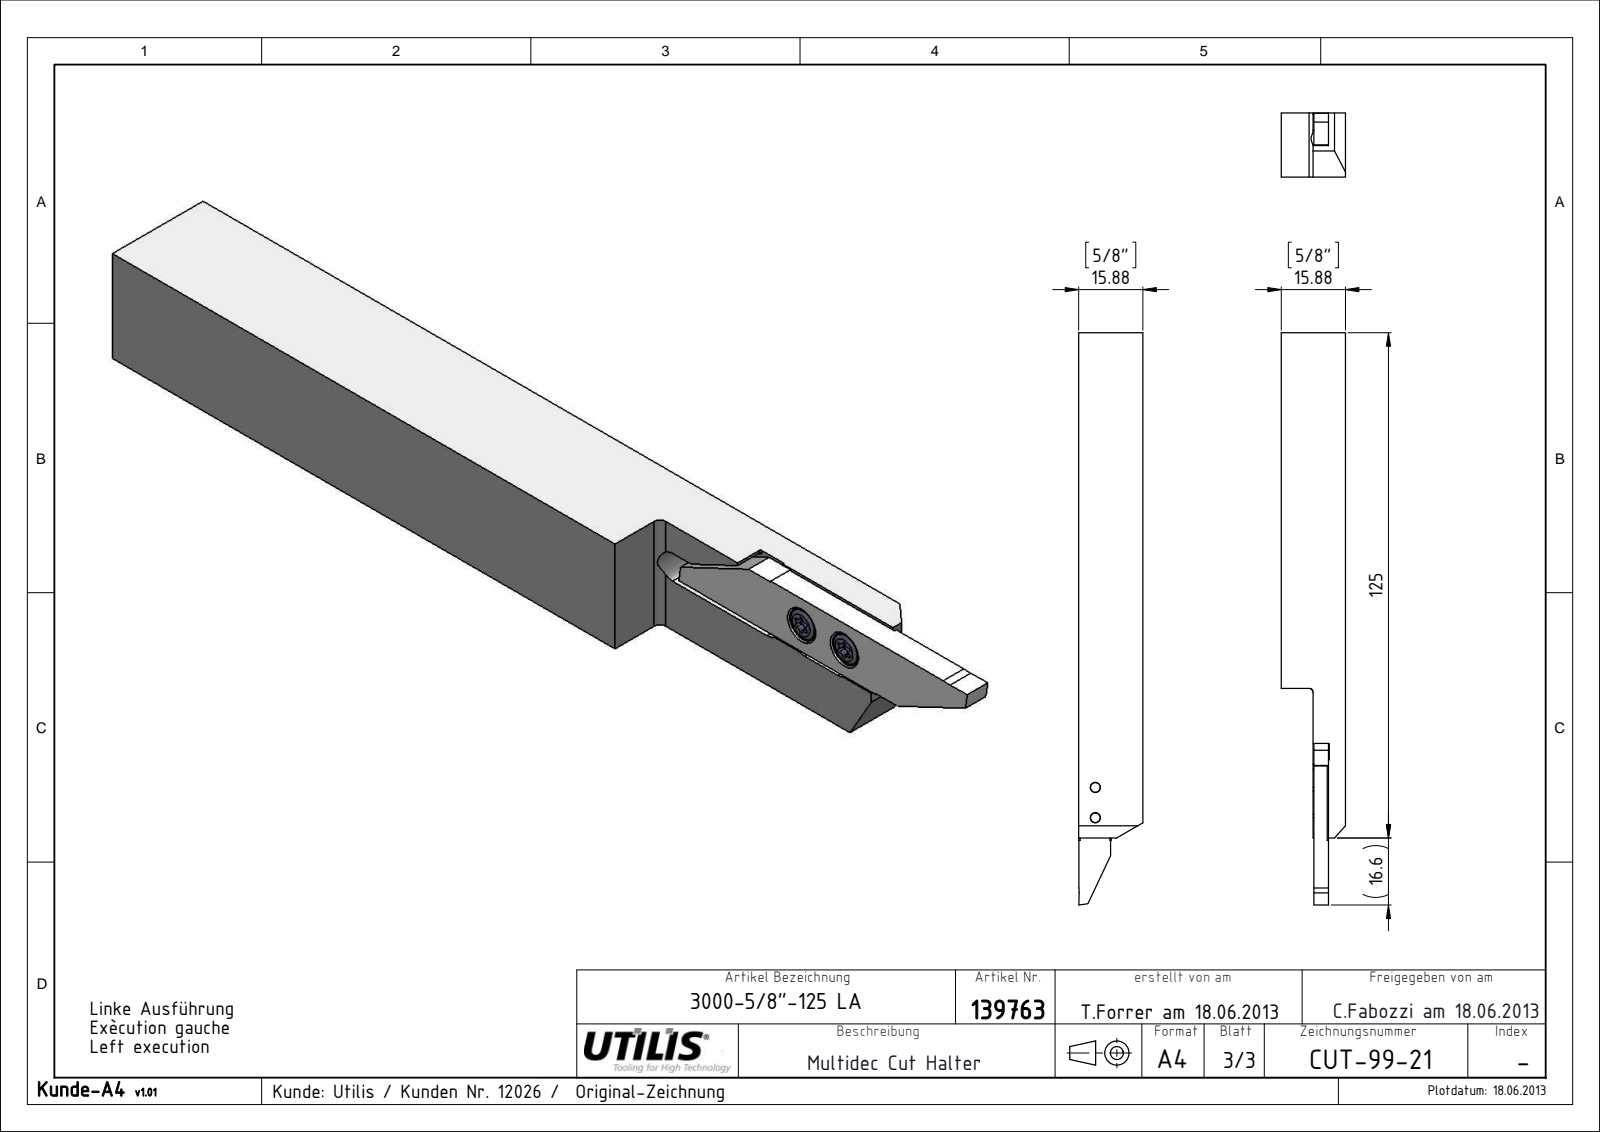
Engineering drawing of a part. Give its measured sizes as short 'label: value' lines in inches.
name: CUT-99-Kunde_3000-5-8-125 LA; CUT-99-Kunde_-_3000-5-8-125 LA; MSP-16_M3x7.3 T08; CUT-3000 R-L Kunde Lang_Lang
written by: SolidWorks 2013 (CONFIG_CONTROL_DESIGN)
unit: in
bodies: 4 solids, 141 faces (45 planar, 56 cylindrical, 40 other)
size: 5.575 × 0.625 × 0.625
volume: 1.642 in³; area: 14.23 in²
holes: 2× ⌀0.098, 2× ⌀0.14
bosses: 2× ⌀0.161, 2× ⌀0.118
rounds: 12× R0.008, 12× R0.018, 4× R0.083, 2× R0.006, 2× R0.394, 1× R0.039
face distances: 0.625, 0.625, 0.165, 0.459, 0.315, 0.15, 0.318, 0.142, 0.307, 0.31
hole spacings: 0.295, 0.291, 0.299
